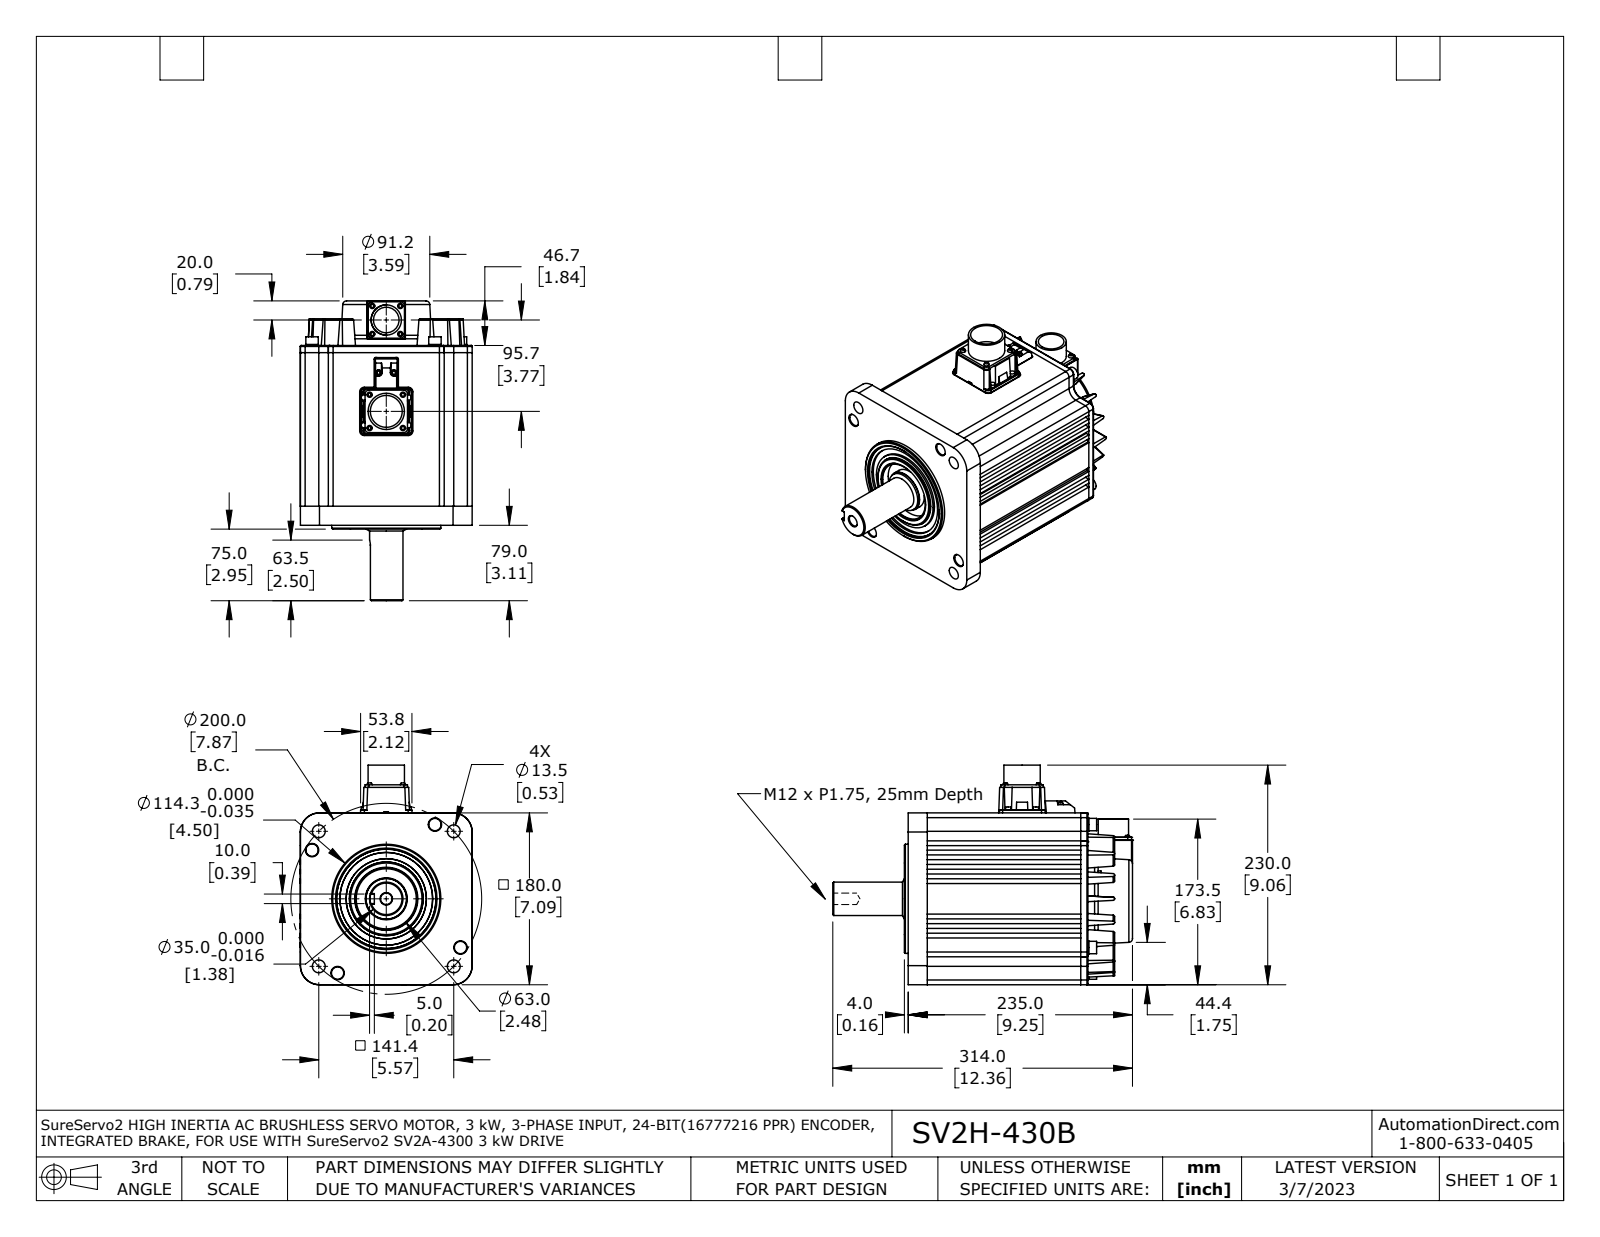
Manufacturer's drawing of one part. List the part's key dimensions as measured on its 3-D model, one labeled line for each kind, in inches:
Part name (STEP PRODUCT): SV2M-x30B fxt
STEP written by: SolidWorks 2021 (AUTOMOTIVE_DESIGN)
Units: inches
Bodies: 1 solid, 632 faces (336 planar, 203 cylindrical, 93 other)
Overall size (bounding box): 12.362 × 9.056 × 7.087
Volume: 366.2 in³ · Surface area: 491 in²
Round holes (diameter × count): ⌀0.531 ×4, ⌀0.551 ×4, ⌀0.472 ×1, ⌀1.058 ×1, ⌀1.317 ×1, ⌀2.48 ×1
Round bosses / shafts (diameter × count): ⌀0.217 ×7, ⌀0.528 ×4, ⌀0.512 ×4, ⌀0.315 ×4, ⌀0.236 ×2, ⌀4.567 ×1, ⌀4.5 ×1, ⌀1.732 ×1
Partial cylindrical surfaces — rounded edges, fillets, slot ends (radius × count): R0.197 ×17, R0.064 ×16, R0.157 ×16, R0.039 ×12, R0.02 ×4, R0.191 ×4, R0.394 ×4, R0.787 ×4
Main face-to-face distances: 0.197, 7.087, 0.394, 1.154, 5.933, 0.591, 3.031, 7.413, 3.228, 2.835
Hole centre spacings: 0.824, 3.661, 3.937, 4.8, 5.178, 5.568, 5.897, 7.559
